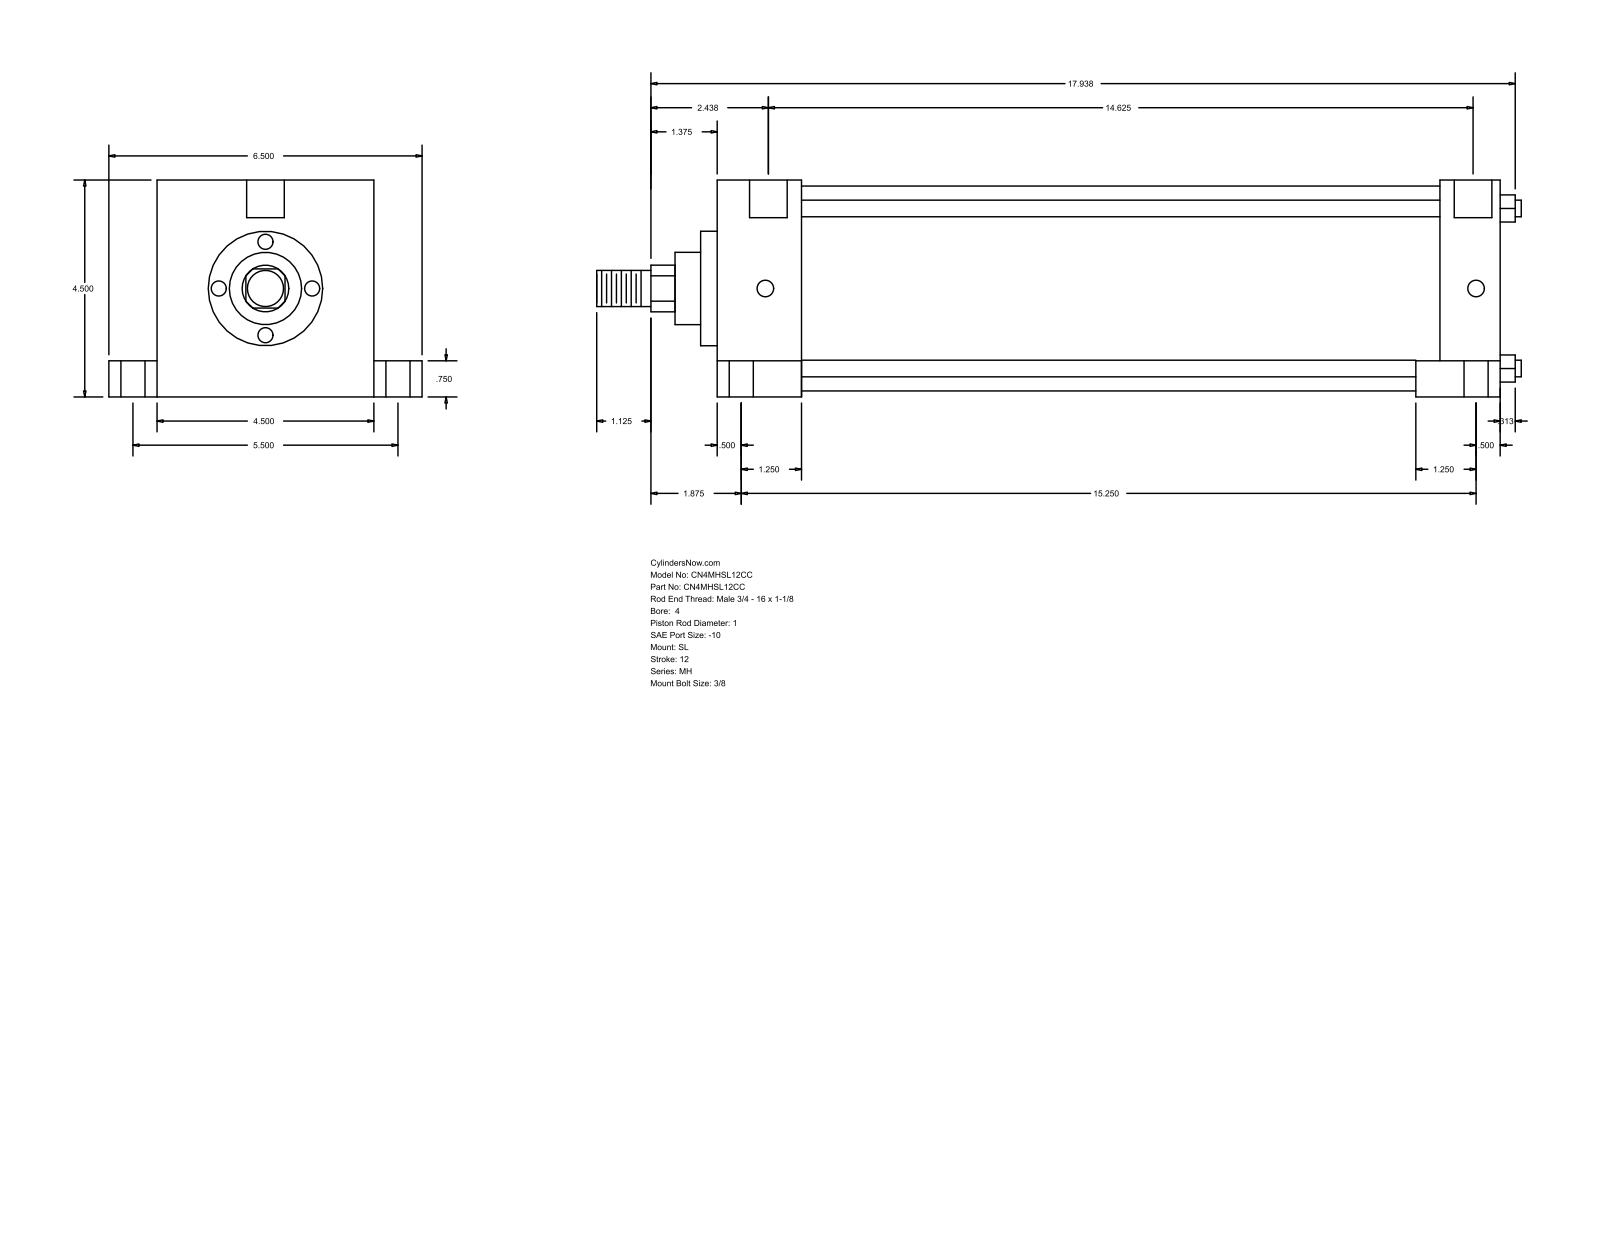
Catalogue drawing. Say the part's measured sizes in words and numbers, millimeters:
The part is named "MH_SL__0400_1". Its 3-D file was written by "GSSL Pune (CONFIG_CONTROL_DESIGN)". It is 0 solids with 110 faces: 77 planar, 33 cylindrical and 0 other. Overall it measures 487.36 by 165.1 by 114.3 millimeters. Round holes: 4 of diameter 8.73, 4 of diameter 12.7, 4 of diameter 19.05, 2 of diameter 19.84. Round bosses or shafts: 4 of diameter 8.76, 1 of diameter 107.95, 1 of diameter 60.33, 1 of diameter 38.1, 1 of diameter 25.4, 1 of diameter 19.05. Partial cylindrical surfaces (rounded edges, fillets, slot ends): 1 of radius 12.29. The main face-to-face distances are 114.3, 412.76, 44.46, 368.3, 381.01, 336.55, 31.75, 25.4, 139.7, 19.05. The hole center spacings are 69.85, 69.87, 71, 71.3, 139.7, 374.65, 379.55, 381.11.
